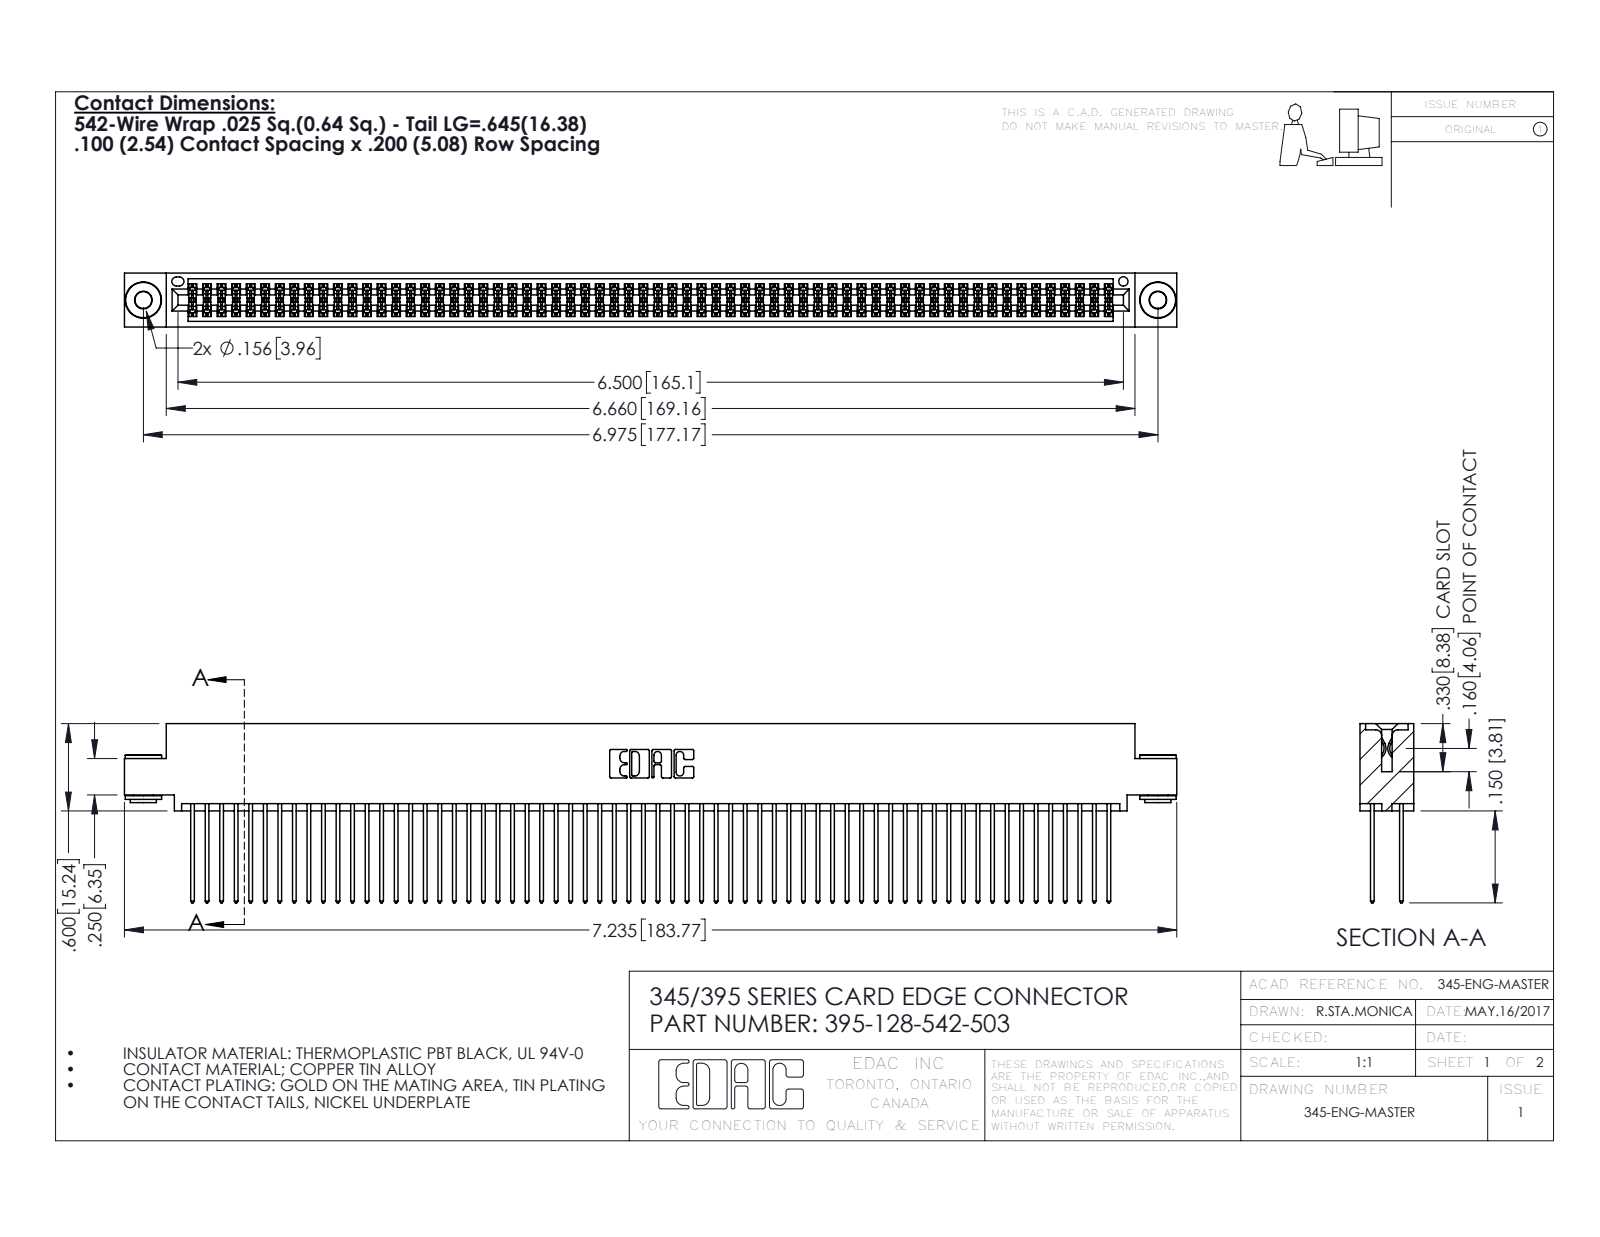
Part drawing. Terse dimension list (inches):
name: 395-128-542-503; 345-292-001_345-293-142; 345-250-002_345-250-002-102; 345 Part_0.110 Offset - 0.156 Dia-TH
written by: SolidWorks 2016 (CONFIG_CONTROL_DESIGN)
unit: in
bodies: 131 solids, 6568 faces (4318 planar, 2242 cylindrical, 8 other)
size: 7.235 × 1.232 × 0.37
volume: 1.135 in³; area: 48.06 in²
holes: 2× ⌀0.116, 2× ⌀0.156, 1× ⌀0.064
bosses: 2× ⌀0.25, 2× ⌀0.18, 2× ⌀0.136
rounds: 192× R0.006, 128× R0.01, 22× R0.01, 6× R0.007, 6× R0.031, 3× R0.026, 2× R0.014, 2× R0.019
face distances: 0.072, 0.298, 0.2, 0.025, 0.098, 0.272, 0.225, 0.37, 0.175, 0.149
hole spacings: 0.27, 6.739, 6.975
